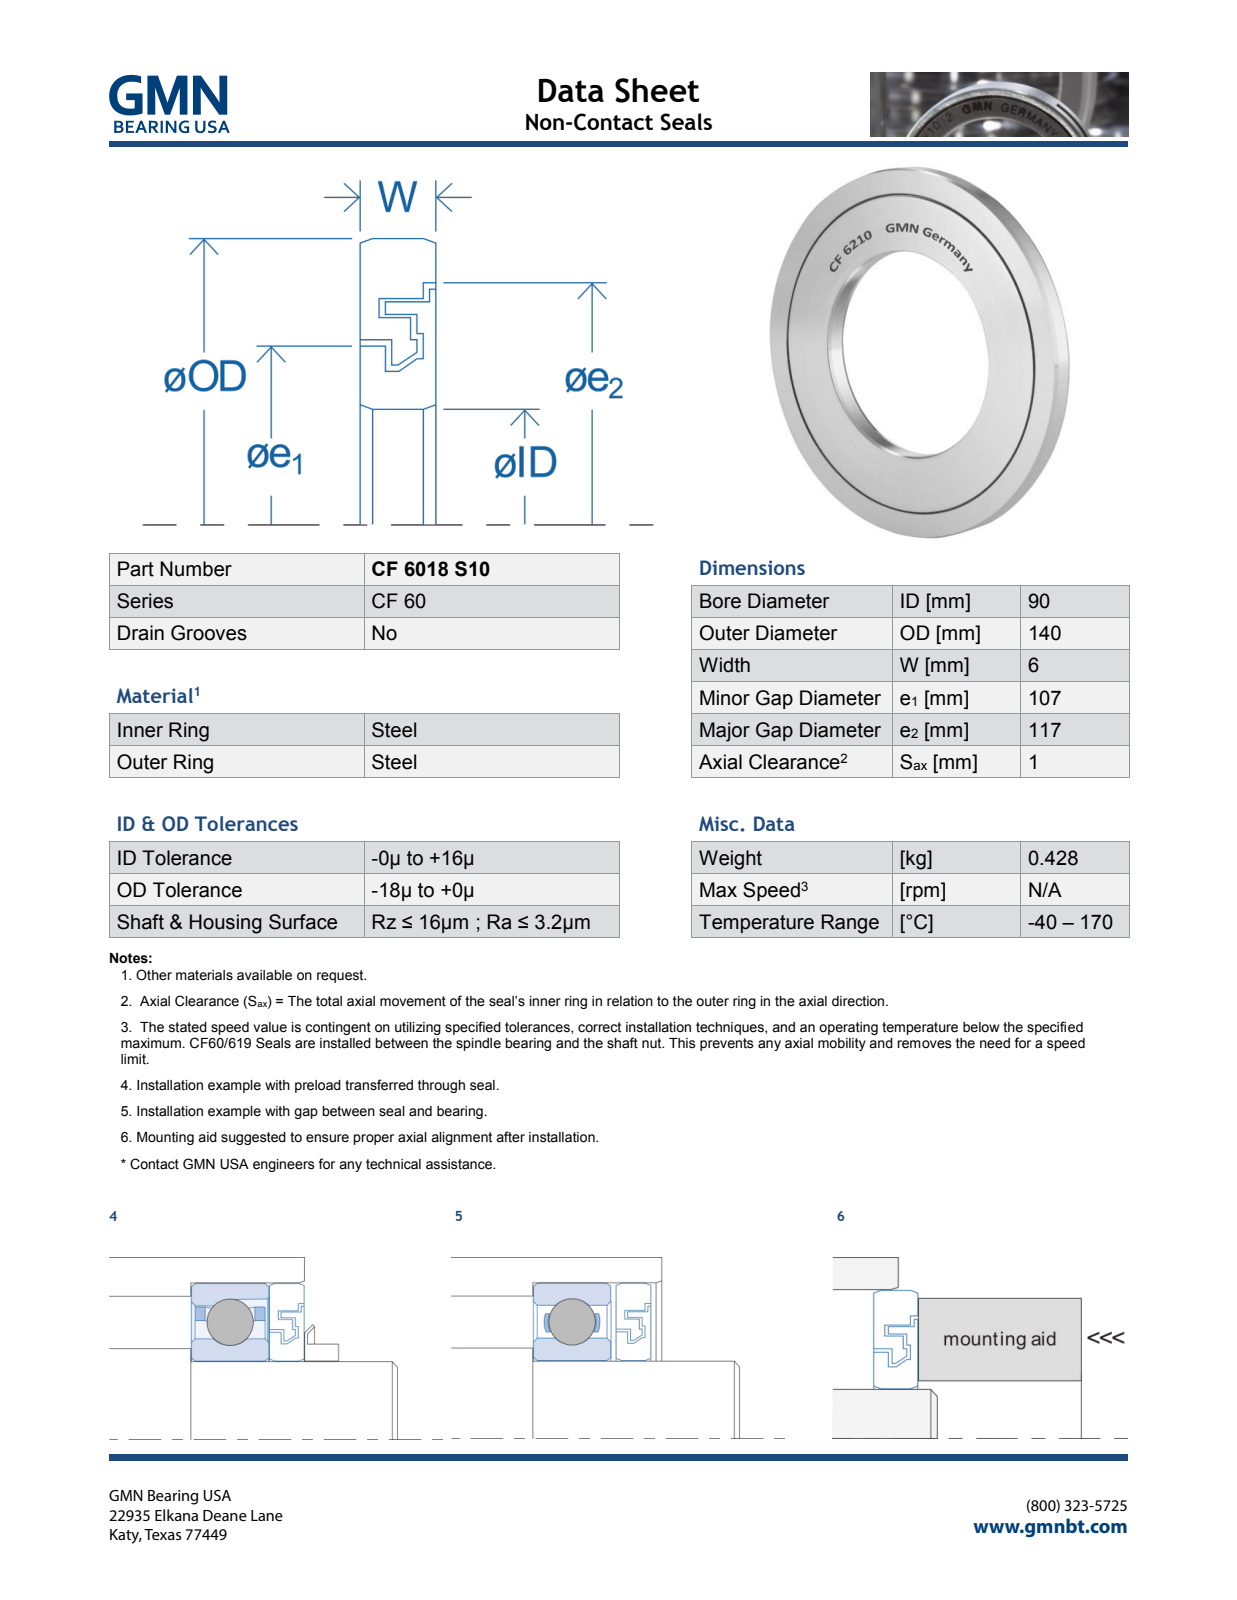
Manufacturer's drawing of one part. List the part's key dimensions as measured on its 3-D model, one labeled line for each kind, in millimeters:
Part name (STEP PRODUCT): CF6018S10_PRT
STEP written by: PRO/ENGINEER BY PARAMETRIC TECHNOLOGY CORPORATION, 2013150 (AUTOMOTIVE_DESIGN)
Units: millimetres
Bodies: 2 solids, 676 faces (634 planar, 30 cylindrical, 12 other)
Overall size (bounding box): 140 × 140 × 6.05
Volume: 51 095 mm³ · Surface area: 35 302 mm²
Round holes (diameter × count): ⌀90 ×1, ⌀104 ×1, ⌀108 ×1, ⌀109 ×1, ⌀112 ×1, ⌀114.5 ×1, ⌀117 ×1
Round bosses / shafts (diameter × count): ⌀140 ×1, ⌀116 ×1, ⌀114 ×1, ⌀111.5 ×1, ⌀107 ×1, ⌀105 ×1, ⌀103 ×1
Main face-to-face distances: 6, 0.5, 2, 2.5, 1, 1.5, 4, 3, 3.5, 4.5
